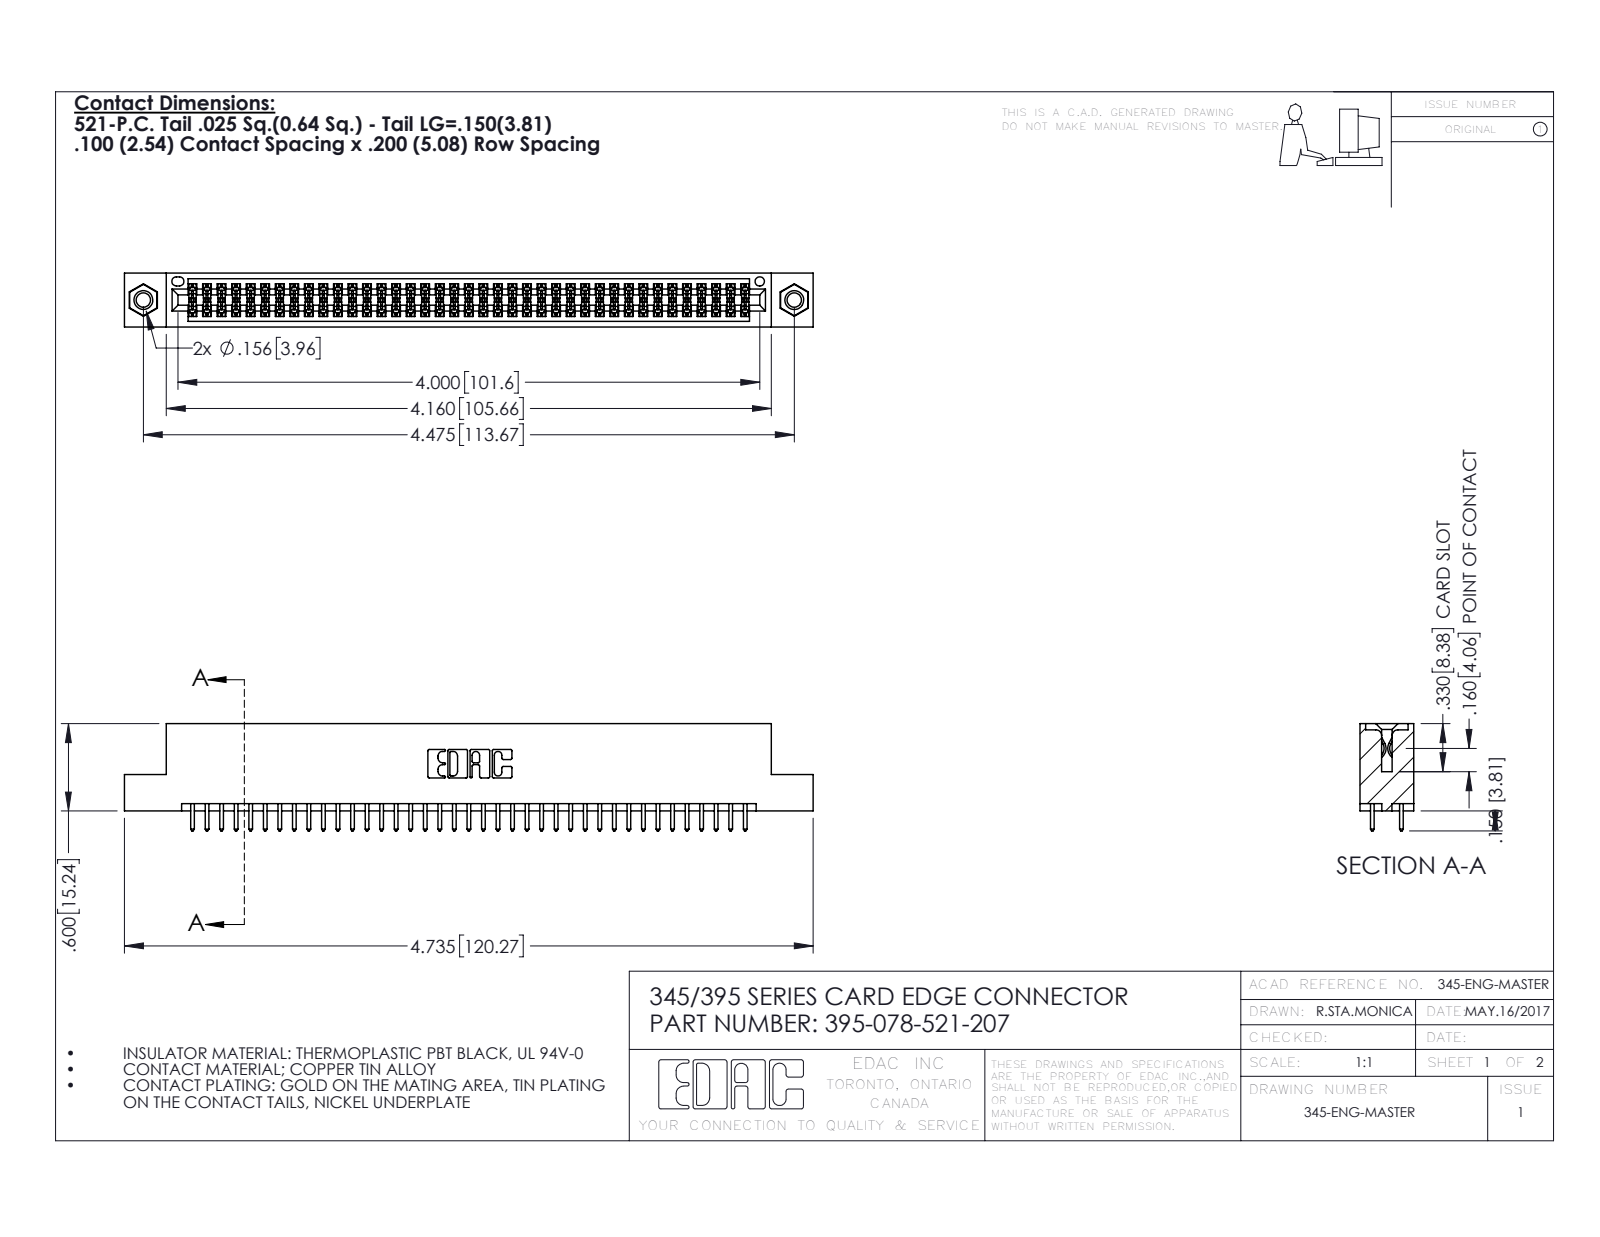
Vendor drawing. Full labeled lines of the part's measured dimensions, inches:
Part name (STEP PRODUCT): 345 Part_Flush Mounting Lugs - 0.156 Dia-TI; 345-292-001_345-293-121; 345-250-001_345-250-005-103; 395-078-521-207
STEP written by: SolidWorks 2016 (CONFIG_CONTROL_DESIGN)
Units: inches
Bodies: 81 solids, 4086 faces (2686 planar, 1384 cylindrical, 16 other)
Overall size (bounding box): 4.735 × 0.737 × 0.37
Volume: 0.708 in³ · Surface area: 26.23 in²
Round holes (diameter × count): ⌀0.098 ×2, ⌀0.125 ×2, ⌀0.156 ×2, ⌀0.064 ×1
Round bosses / shafts (diameter × count): ⌀0.155 ×2
Partial cylindrical surfaces — rounded edges, fillets, slot ends (radius × count): R0.006 ×117, R0.01 ×78, R0.01 ×22, R0.007 ×6, R0.031 ×6, R0.026 ×3, R0.014 ×2, R0.019 ×2
Main face-to-face distances: 0.072, 0.298, 0.2, 0.37, 0.098, 0.272, 0.025, 0.225, 0.175, 0.149
Hole centre spacings: 0.27, 4.239, 4.475
